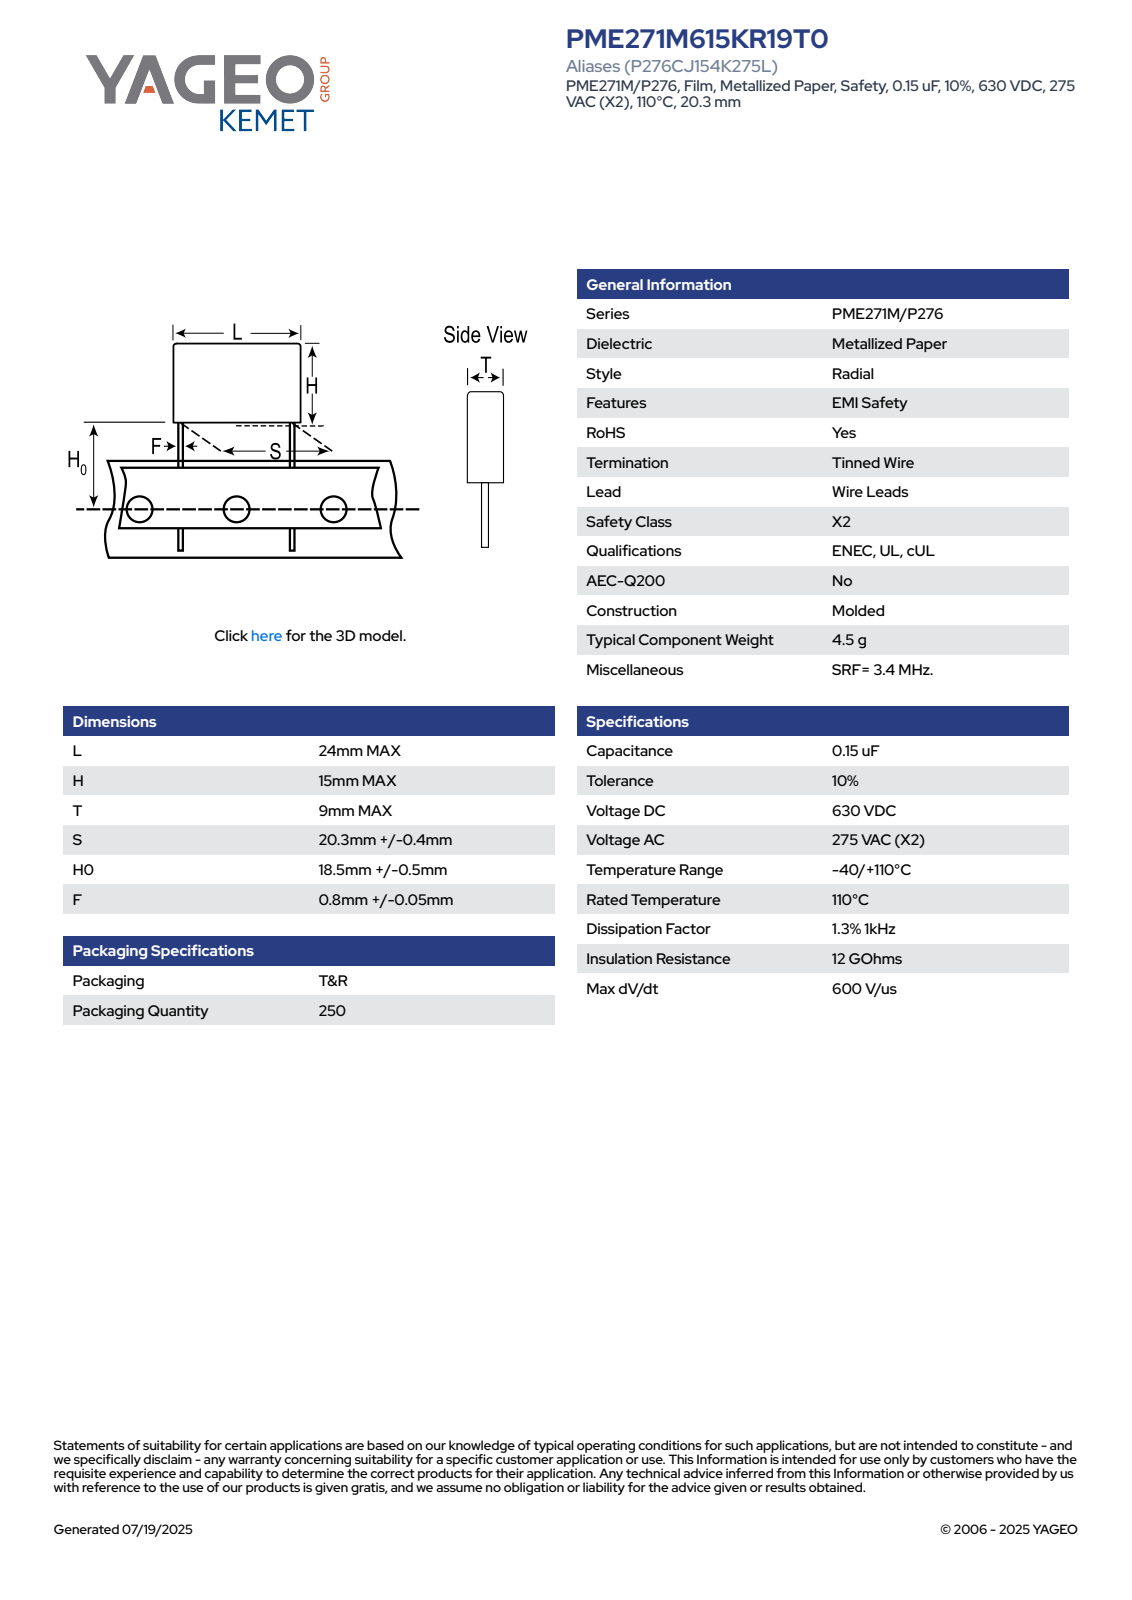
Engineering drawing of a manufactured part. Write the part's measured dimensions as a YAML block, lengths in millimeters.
part_name: "CFR_MOLDED_24X15X9_L24H15T9S20.3H019F0.85"
step_written_by: "SolidWorks 2014 (AUTOMOTIVE_DESIGN)"
units: millimeters
bodies: {solids: 4, faces: 73, planar: 65, cylindrical: 8, other: 0}
overall_size: [34, 24, 9.01]
volume: 3258
surface_area: 1537
round_bosses_or_shafts:
  - {diameter: 0.85, count: 2}
partial_cylinders:
  - {radius: 0.5, count: 4}
face_to_face_distances: [9, 15, 24, 19, 34, 27.44, 8.44, 6.56, 25.29, 6.29]
